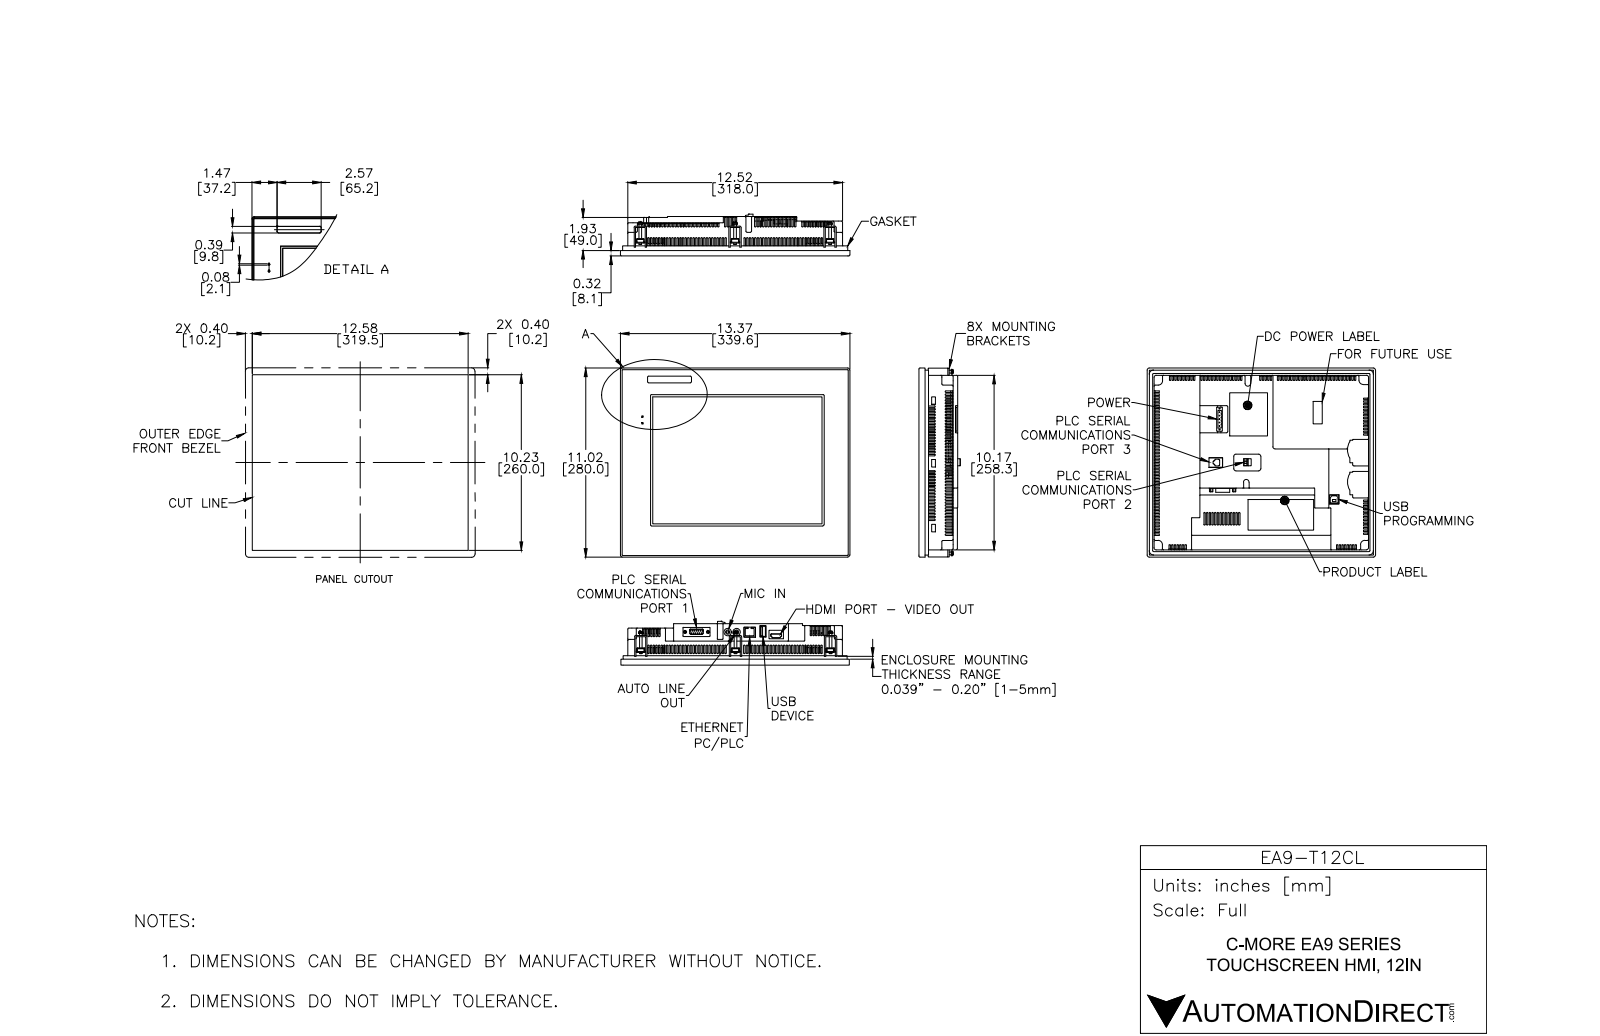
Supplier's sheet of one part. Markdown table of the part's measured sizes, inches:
| quantity | value |
| --- | --- |
| part name | EA9-T12CL |
| STEP written by | SolidWorks 2014 (AUTOMOTIVE_DESIGN) |
| units | inches |
| bodies | 4 solids, 2787 faces (1448 planar, 1240 cylindrical, 99 other) |
| overall size | 13.307 × 11.024 × 2.578 |
| volume | 54.58 in³ |
| surface area | 908.3 in² |
| round holes (diameter × count) | 0.045 × 12, 0.07 × 2, 0.08 × 2, 0.045 × 1, 0.13 × 1, 0.14 × 1, 0.435 × 1, 0.435 × 1 |
| round bosses / shafts (diameter × count) | 0.05 × 5, 0.25 × 2 |
| partial cylindrical surfaces (radius × count) | 0.042 × 316, 0.04 × 101, 0.043 × 72, 0.031 × 67, 0.045 × 50, 0.062 × 46, 0.038 × 28, 0.02 × 19 |
| main face-to-face distances | 0.05, 0.1, 2.369, 0.099, 0.26, 2.109, 0.049, 0.31, 2.059, 0.15 |
| hole center spacings | 0.115, 0.229, 0.148, 0.219, 0.15, 0.344, 0.222, 0.229 |
